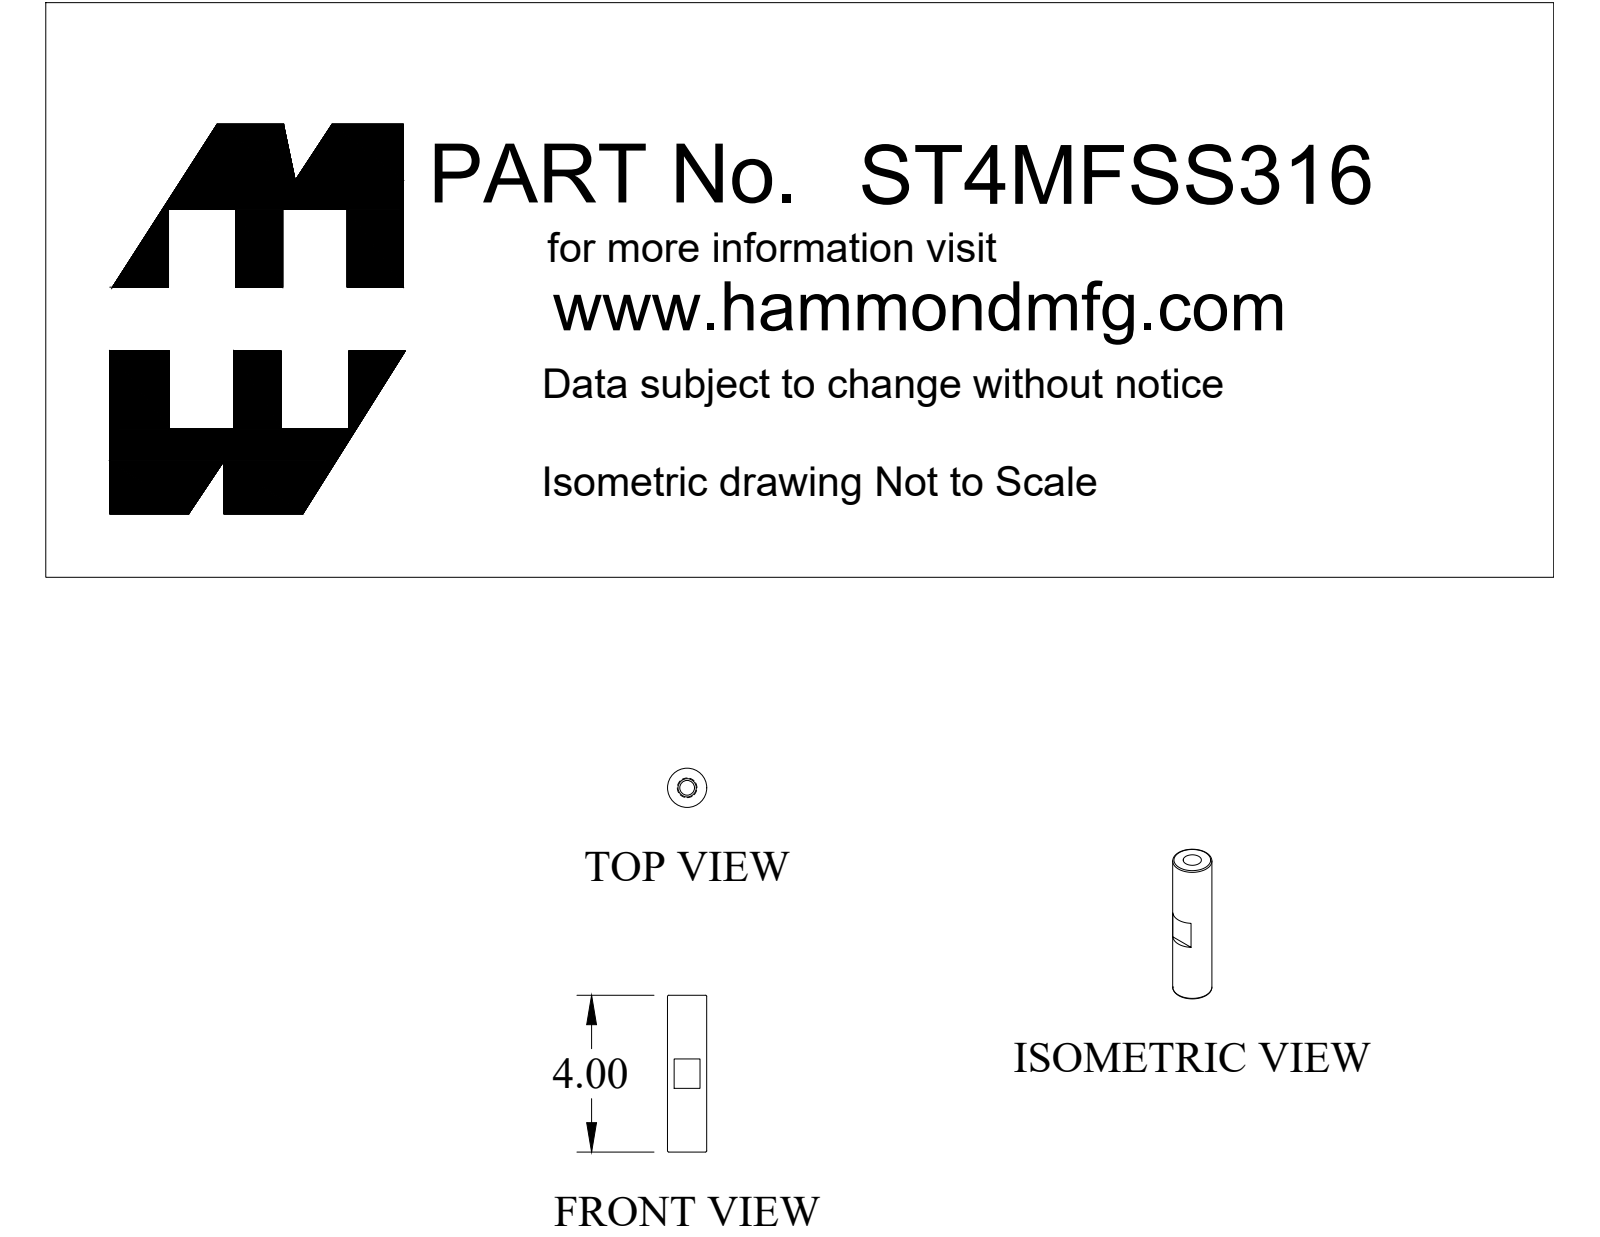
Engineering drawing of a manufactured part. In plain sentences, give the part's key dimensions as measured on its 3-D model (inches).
The part is named "ST4MFSS316". Its 3-D file was written by "SolidWorks 2019 (CONFIG_CONTROL_DESIGN)". It is 3 solids with 31 faces: 21 planar, 7 cylindrical and 3 other. Overall it measures 4.418 by 1 by 1 inches. Its volume is 2.878 cubic inches and its surface area 23.61 square inches. Round holes: 1 of diameter 0.375, 1 of diameter 0.465, 1 of diameter 0.532. Round bosses or shafts: 1 of diameter 1, 1 of diameter 0.5. The main face-to-face distances are 0.105, 0.75, 4, 4.105, 4.418, 0.418, 0.313, 0.75, 1.625, 2.375.
